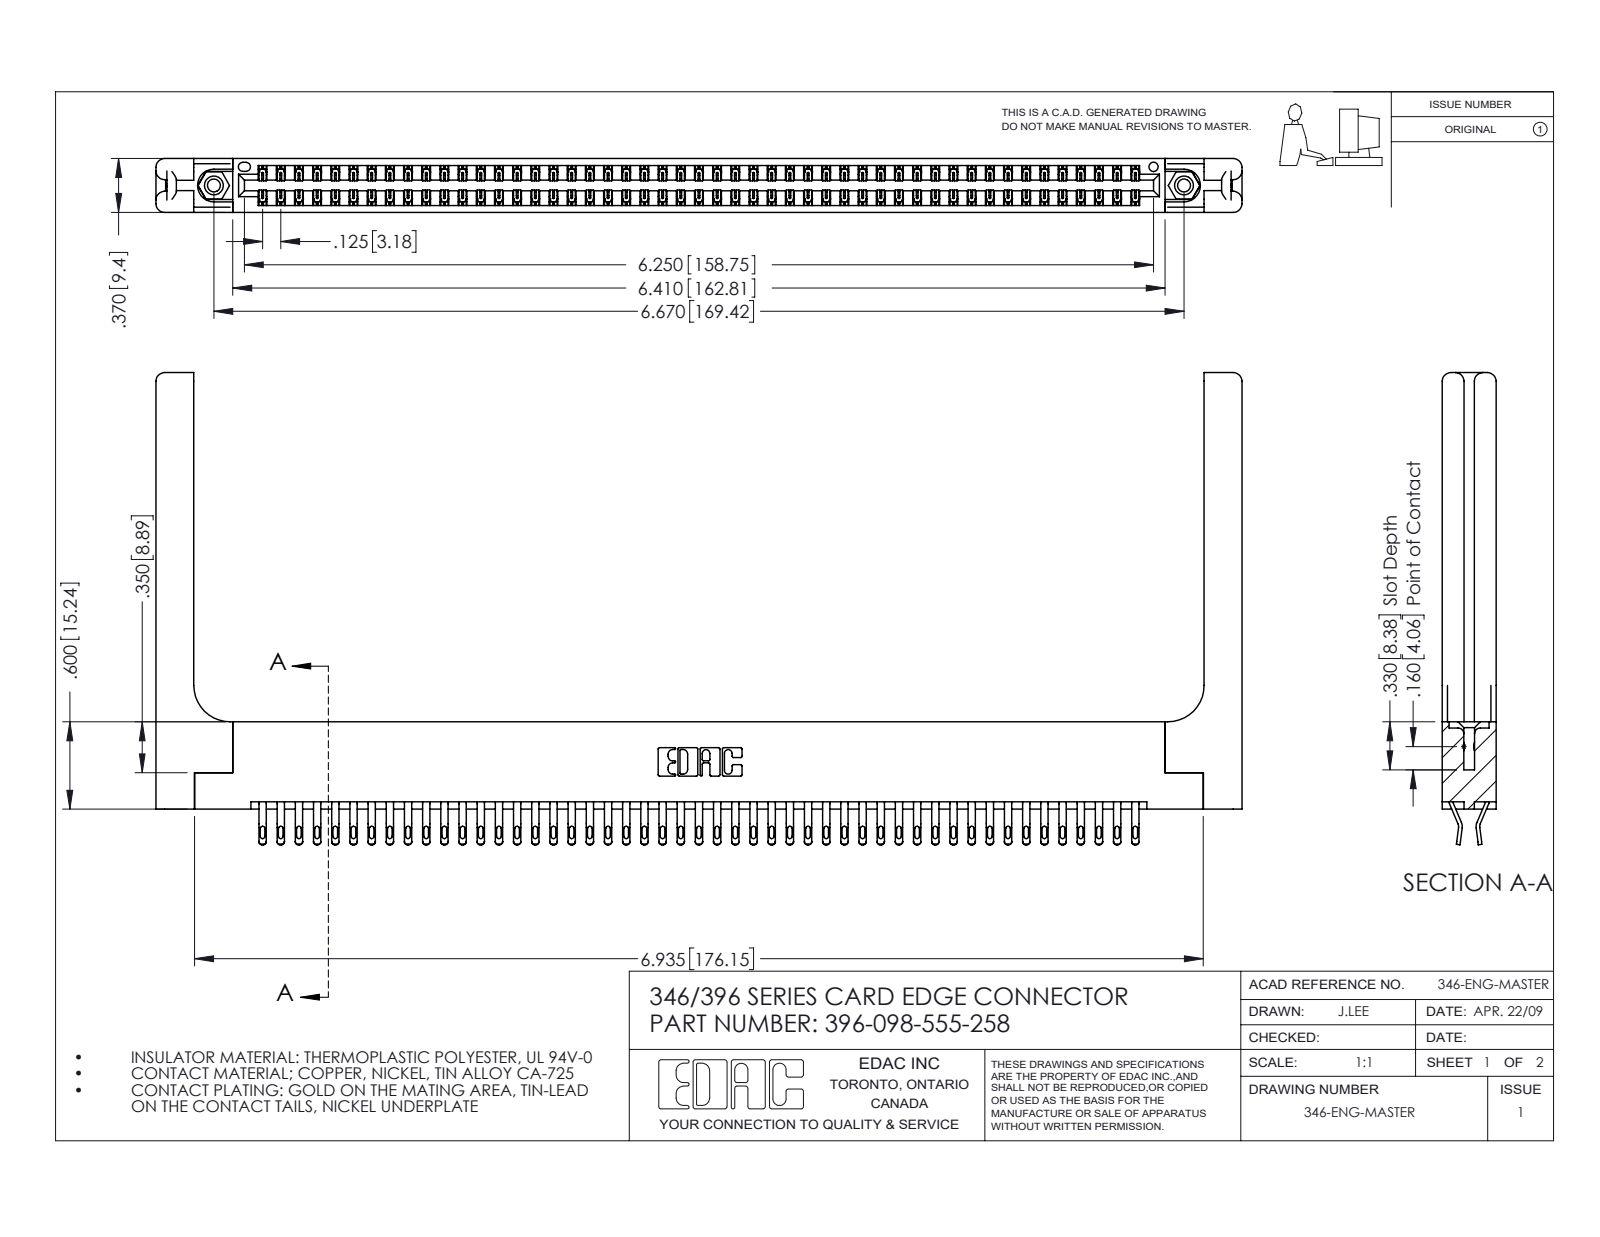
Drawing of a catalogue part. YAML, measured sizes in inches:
part_name: "345-292-001_555 Tail; 346 Part_Flush Mounting Lugs - 0.156 Dia-TH; 396-098-555-258; 345-250-001_345-250-001-102 (+1 more)"
step_written_by: "SolidWorks 2016 (CONFIG_CONTROL_DESIGN)"
units: inches
bodies: {solids: 103, faces: 6062, planar: 3458, cylindrical: 2544, other: 60}
overall_size: [7.466, 3.245, 0.37]
volume: 1.606
surface_area: 49.57
round_holes:
  - {diameter: 0.089, count: 2}
  - {diameter: 0.125, count: 2}
  - {diameter: 0.156, count: 2}
  - {diameter: 0.064, count: 1}
round_bosses_or_shafts:
  - {diameter: 0.155, count: 2}
partial_cylinders:
  - {radius: 0.016, count: 196}
  - {radius: 0.02, count: 196}
  - {radius: 0.006, count: 147}
  - {radius: 0.01, count: 22}
  - {radius: 0.06, count: 16}
  - {radius: 0.007, count: 6}
  - {radius: 0.031, count: 6}
  - {radius: 0.026, count: 3}
face_to_face_distances: [0.37, 0.048, 0.322, 0.072, 0.148, 0.15, 0.25, 0.025, 0.298, 0.275]
hole_center_spacings: [0.246, 6.461, 6.67]
